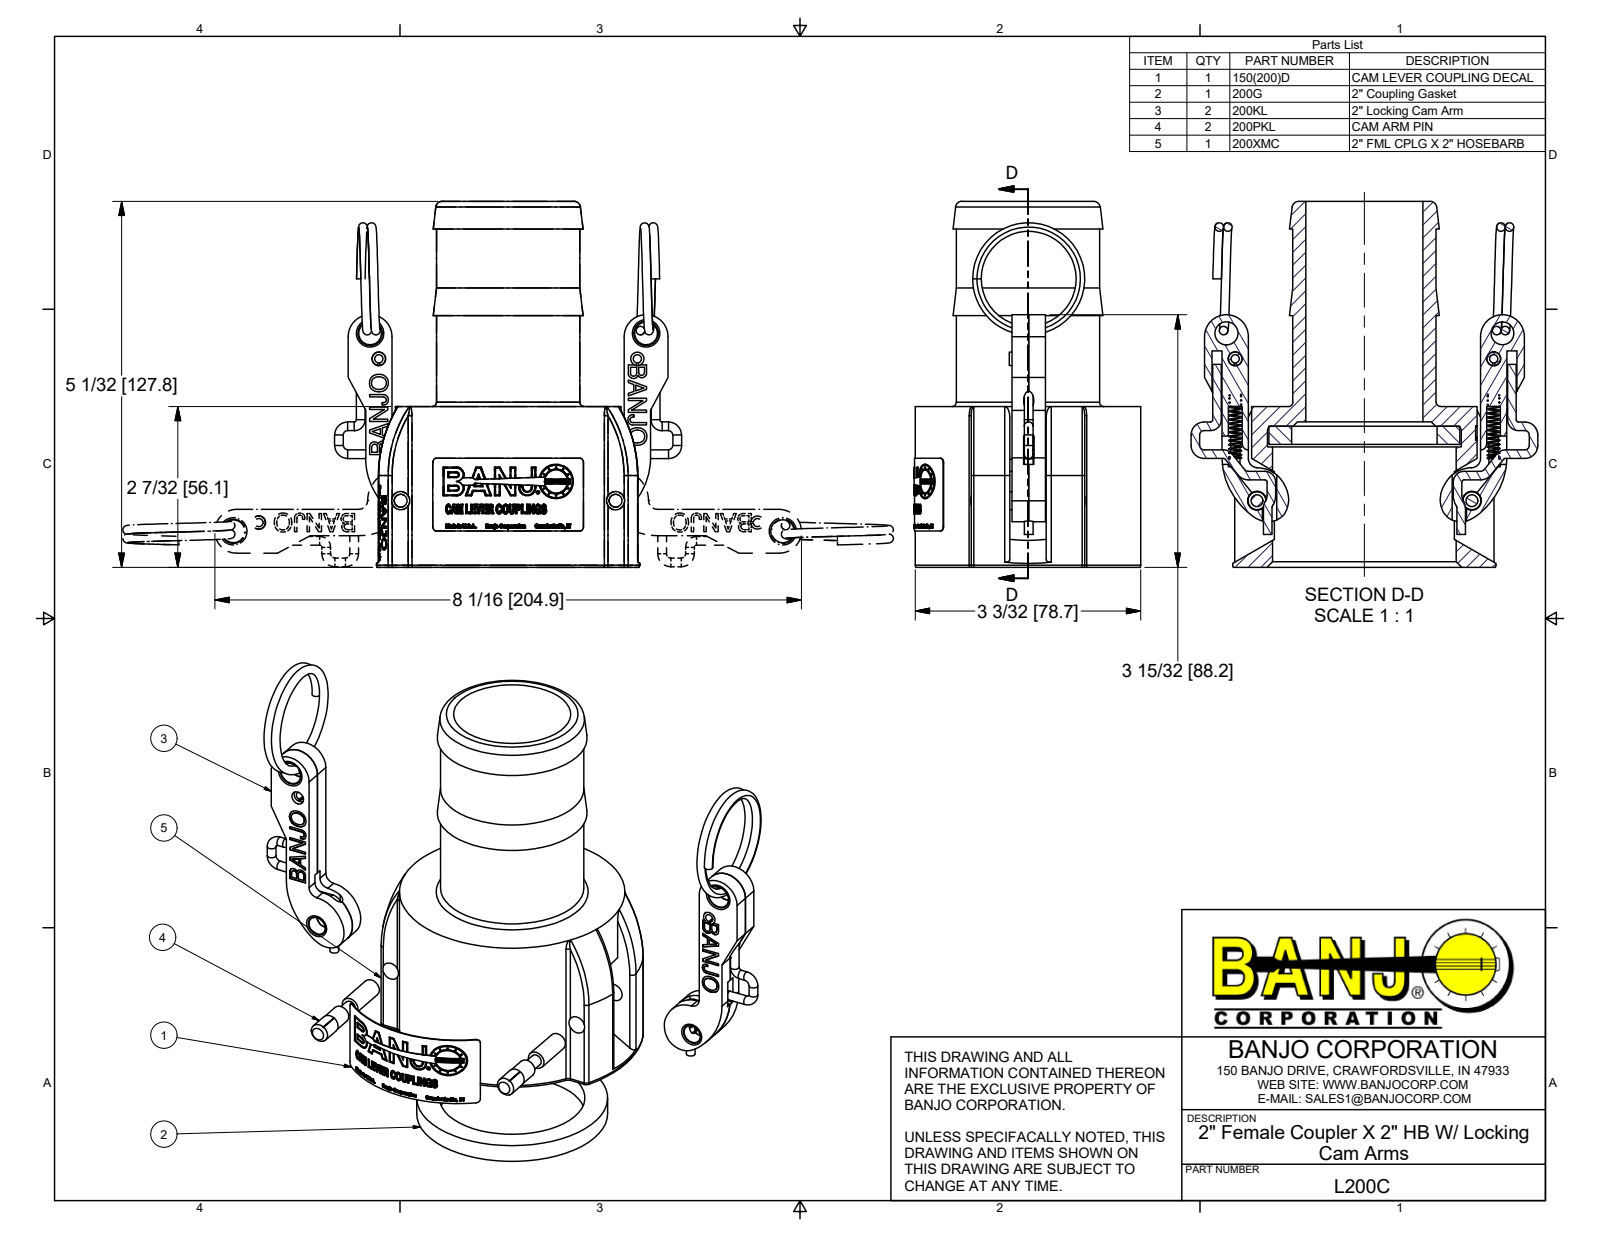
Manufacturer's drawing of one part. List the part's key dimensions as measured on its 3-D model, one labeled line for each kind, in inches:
Part name (STEP PRODUCT): L200C; 200XMC; 200XC; 200KL (+8 more)
STEP written by: Autodesk Inventor 2017 (AUTOMOTIVE_DESIGN)
Units: inches
Bodies: 17 solids, 2115 faces (1001 planar, 309 cylindrical, 805 other)
Overall size (bounding box): 5.03 × 4.771 × 3.115
Volume: 11.89 in³ · Surface area: 133.2 in²
Round holes (diameter × count): ⌀0.114 ×2, ⌀0.14 ×2, ⌀0.187 ×2, ⌀0.19 ×2, ⌀0.25 ×2, ⌀0.315 ×2, ⌀0.318 ×1, ⌀0.449 ×1, ⌀1.61 ×1, ⌀2 ×1, ⌀2.525 ×1, ⌀2.665 ×1
Round bosses / shafts (diameter × count): ⌀0.12 ×15, ⌀0.258 ×2, ⌀0.249 ×2, ⌀0.194 ×2, ⌀0.162 ×2, ⌀3.1 ×1, ⌀2.625 ×1, ⌀1.97 ×1
Partial cylindrical surfaces — rounded edges, fillets, slot ends (radius × count): R0.06 ×18, R0.07 ×6, R0.055 ×4, R0.028 ×2, R0.039 ×2, R0.08 ×2, R0.093 ×2, R0.104 ×2
Main face-to-face distances: 0.27, 2.21, 1.94, 0.25, 0.23, 0.46, 0.23, 0.52, 1.69, 0.53
Hole centre spacings: 0.252, 0.37, 1.776, 1.973, 2.028, 2.338, 3.692, 3.794
